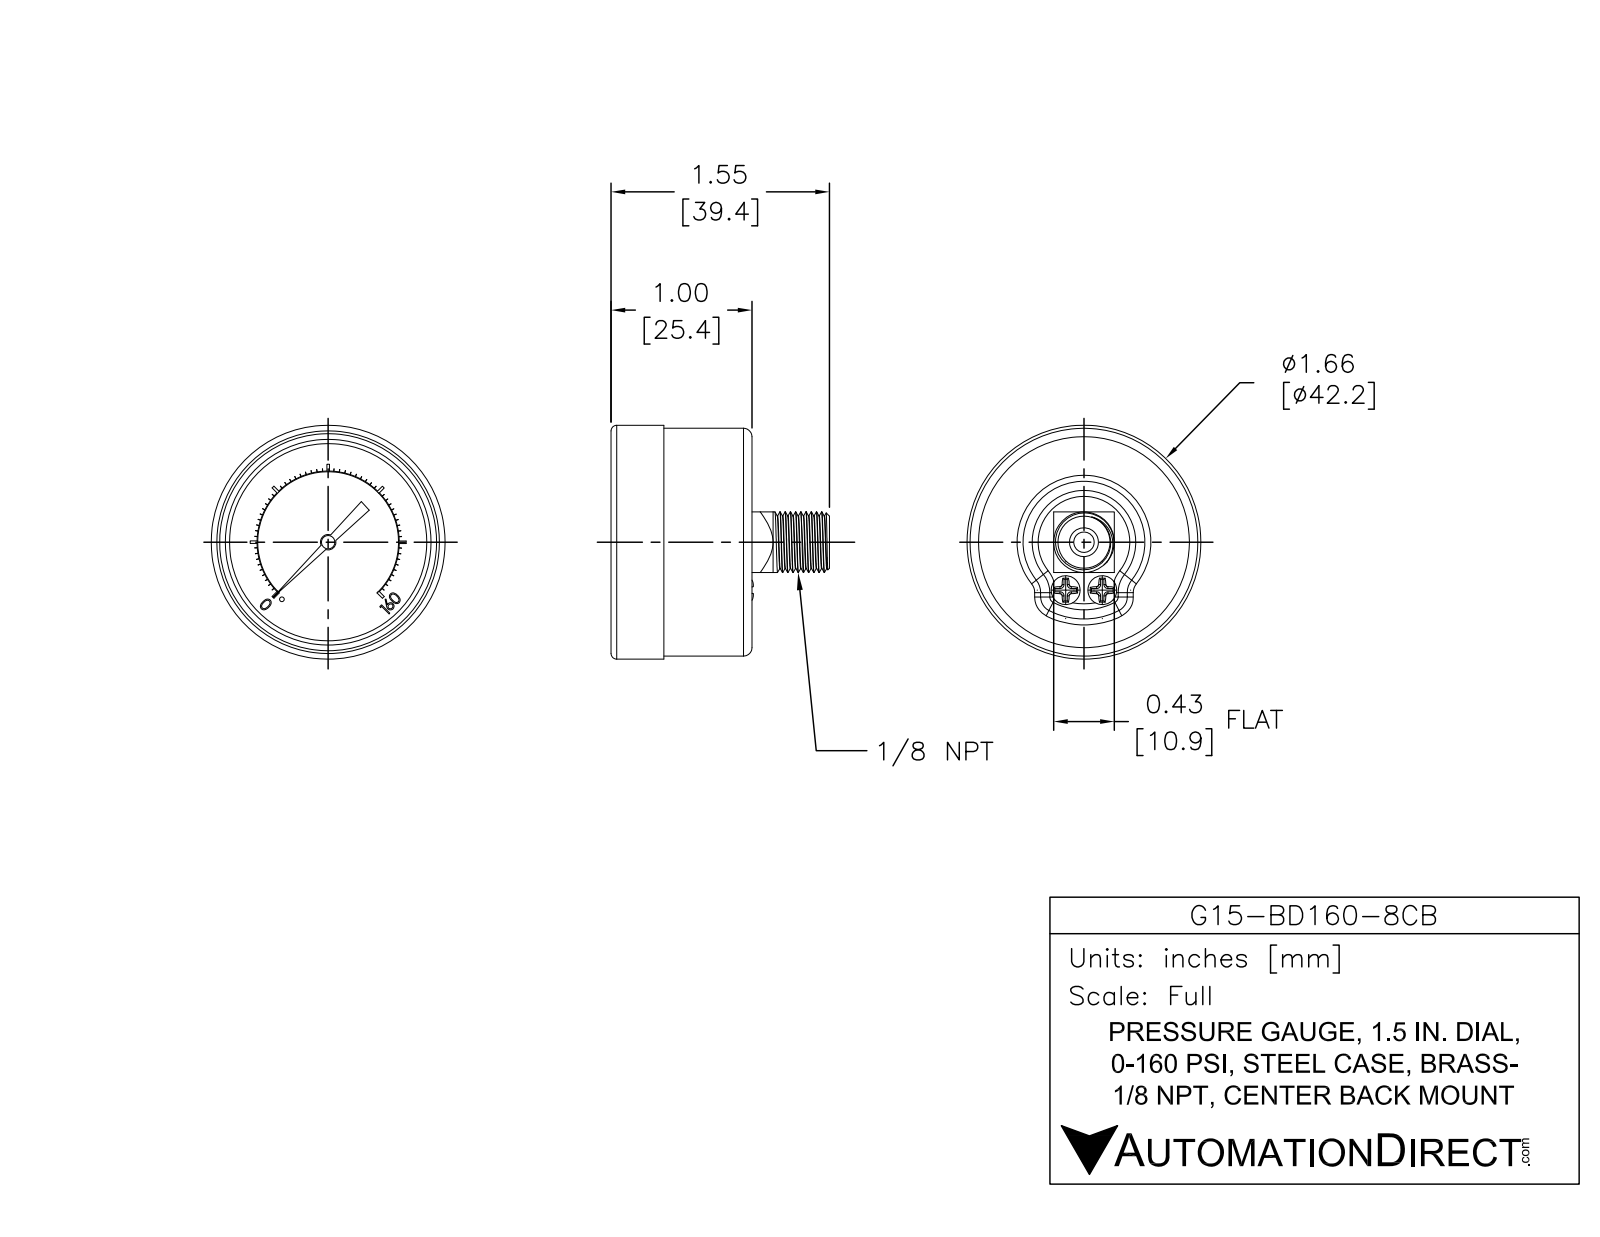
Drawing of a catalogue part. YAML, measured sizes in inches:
part_name: "G15-BD160-8CB"
step_written_by: "SolidWorks 2021 (AUTOMOTIVE_DESIGN)"
units: inches
bodies: {solids: 1, faces: 422, planar: 273, cylindrical: 85, other: 64}
overall_size: [1.66, 1.66, 1.55]
volume: 1.676
surface_area: 12.02
round_holes:
  - {diameter: 0.145, count: 1}
  - {diameter: 1.4, count: 1}
round_bosses_or_shafts:
  - {diameter: 0.205, count: 2}
  - {diameter: 1.66, count: 1}
  - {diameter: 1.617, count: 1}
  - {diameter: 0.43, count: 1}
  - {diameter: 0.086, count: 1}
  - {diameter: 0.06, count: 1}
  - {diameter: 0.033, count: 1}
partial_cylinders:
  - {radius: 0.06, count: 4}
  - {radius: 0.015, count: 2}
  - {radius: 0.048, count: 1}
  - {radius: 0.5, count: 1}
  - {radius: 0.505, count: 1}
face_to_face_distances: [0.71, 0.43, 0.1, 0.61, 0.96, 0.86, 0.25, 0.04, 0.625, 0.525]
